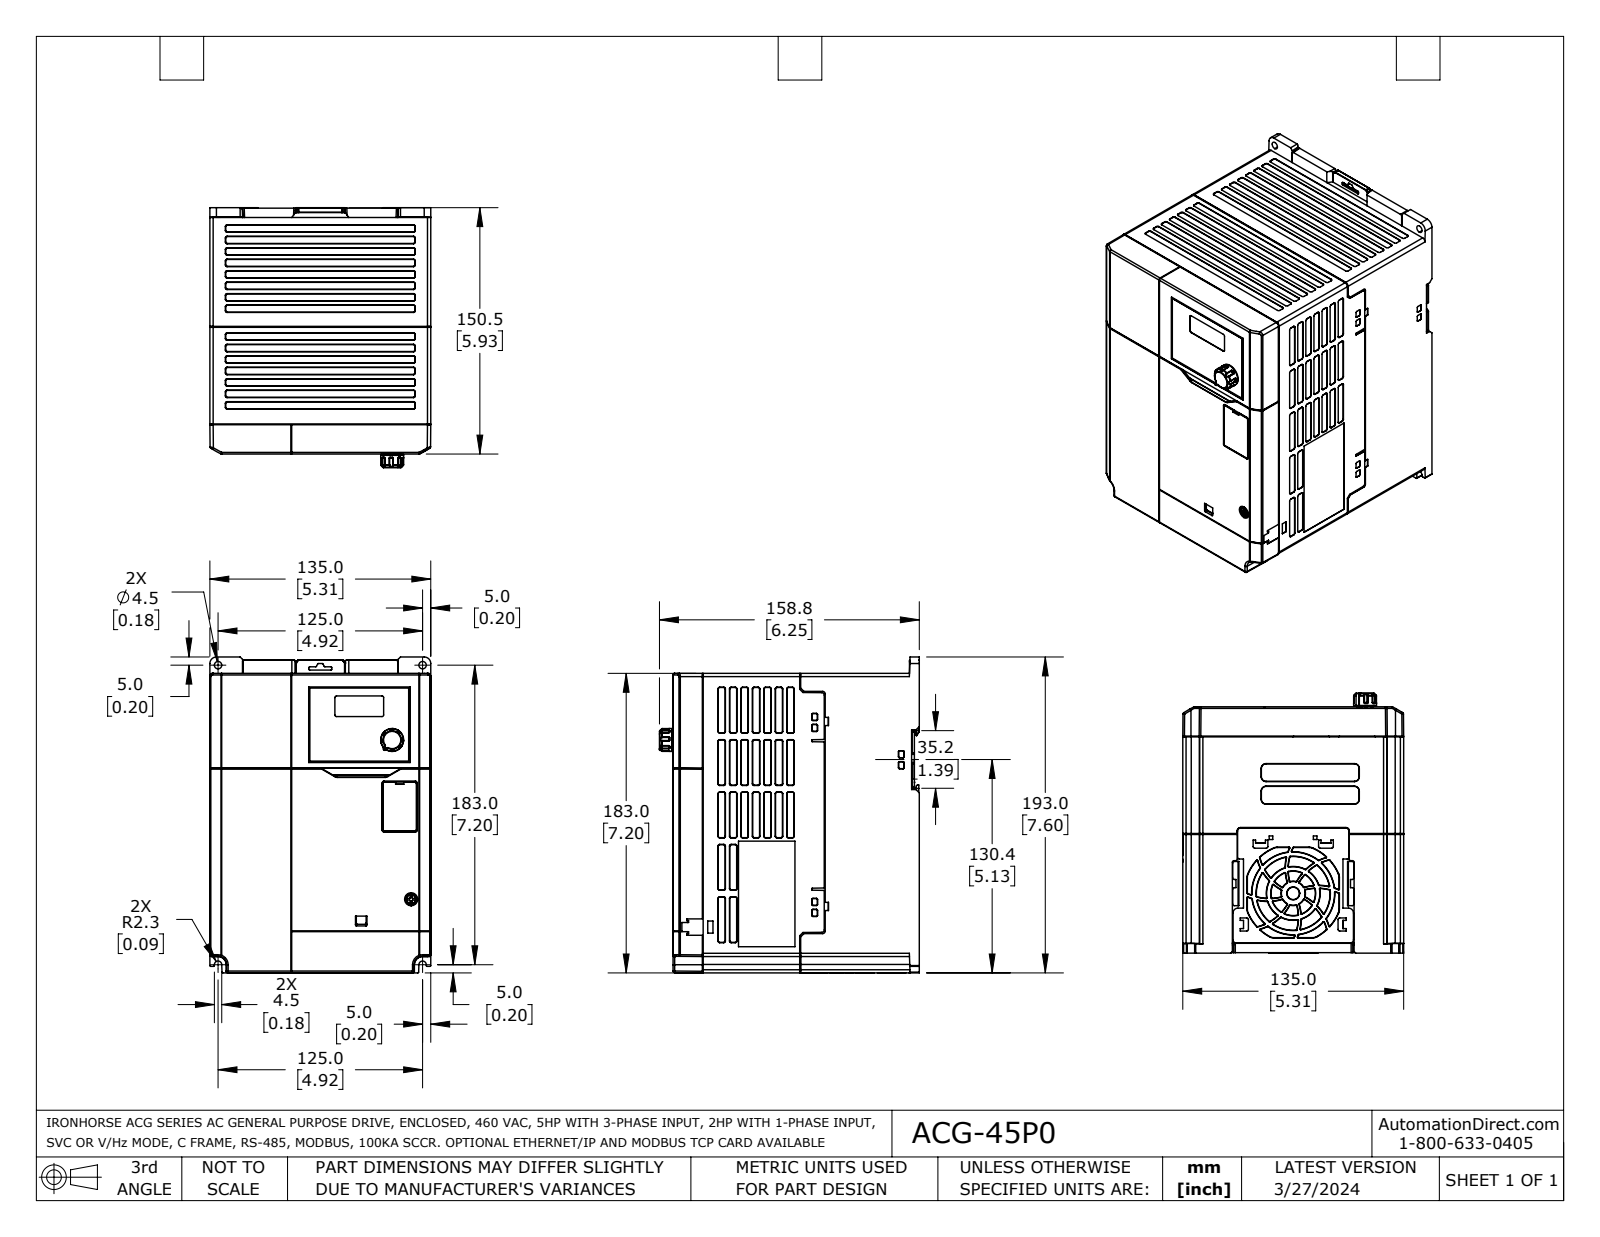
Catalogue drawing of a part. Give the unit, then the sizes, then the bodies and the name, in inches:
Units: inches
Overall size (bounding box): 7.603 × 6.252 × 5.315
Round holes (diameter × count): ⌀0.177 ×2, ⌀0.472 ×2, ⌀0.039 ×1, ⌀0.276 ×1
Round bosses / shafts (diameter × count): ⌀0.551 ×1, ⌀0.543 ×1, ⌀0.236 ×1
Partial cylindrical surfaces — rounded edges, fillets, slot ends (radius × count): R0.008 ×340, R0.02 ×254, R0.039 ×79, R0.012 ×30, R0.079 ×23, R0.031 ×17, R0.059 ×6, R0.016 ×4
Main face-to-face distances: 0.404, 4.911, 4.508, 5.642, 5.807, 5.083, 0.724, 0.165, 4.918, 5.315
Hole centre spacings: 0.273, 0.276, 1.943, 1.944, 2.206, 3.675, 3.858, 3.858
Volume: 73.09 in³ · Surface area: 485.6 in²
Bodies: 4 solids, 4834 faces (2009 planar, 1108 cylindrical, 1717 other)
Part name (STEP PRODUCT): ACG-45P0
STEP written by: SolidWorks 2021 (AUTOMOTIVE_DESIGN)
